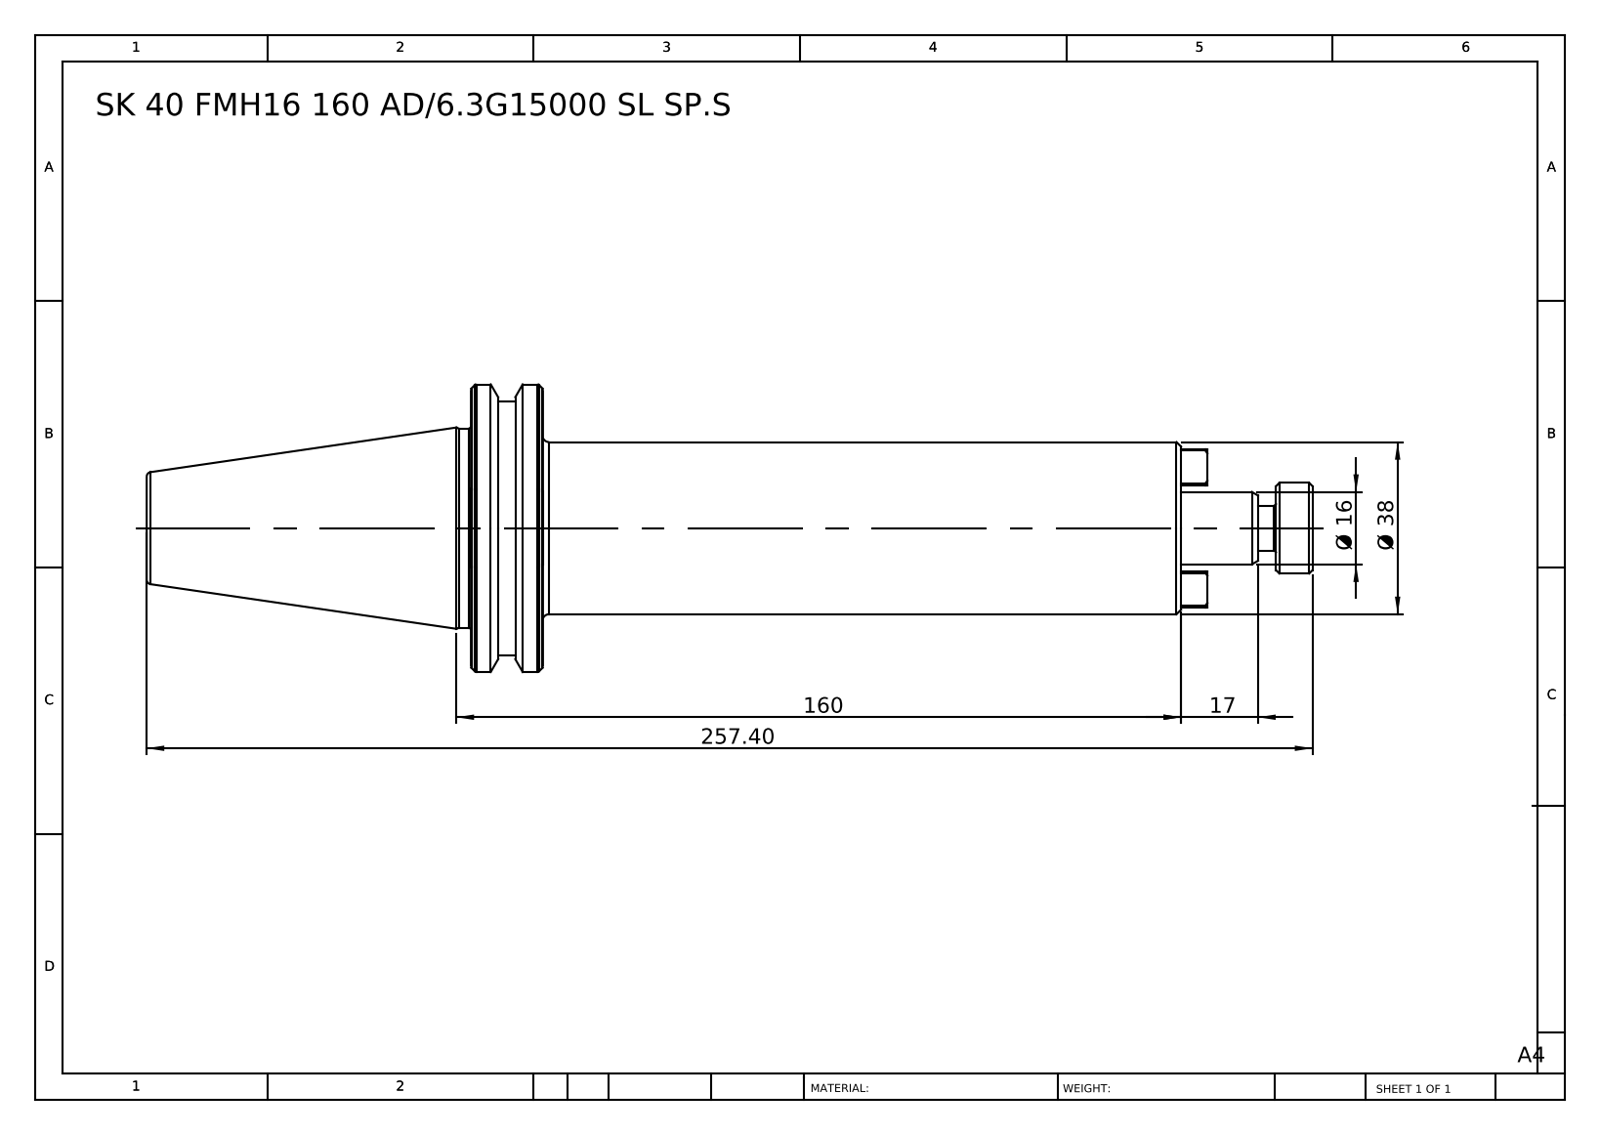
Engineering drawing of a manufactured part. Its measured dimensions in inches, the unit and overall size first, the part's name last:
Units: inches
Overall size (bounding box): 10.134 × 2.5 × 2.5
Round bosses / shafts (diameter × count): ⌀2.5 ×1, ⌀2.205 ×1, ⌀1.732 ×1, ⌀1.496 ×1, ⌀0.787 ×1, ⌀0.63 ×1, ⌀0.394 ×1
Main face-to-face distances: 0.626, 5.547, 6.173, 8.992, 3.445, 2.819, 0.315, 1.142, 6.689, 7.315
Volume: 17.32 in³ · Surface area: 55.54 in²
Bodies: 1 solid, 107 faces (35 planar, 16 cylindrical, 56 other)
Part name (STEP PRODUCT): SK40 FMH16 160 AD-6.3G15000 SL SP.S
STEP written by: SolidWorks 2014 (CONFIG_CONTROL_DESIGN)
